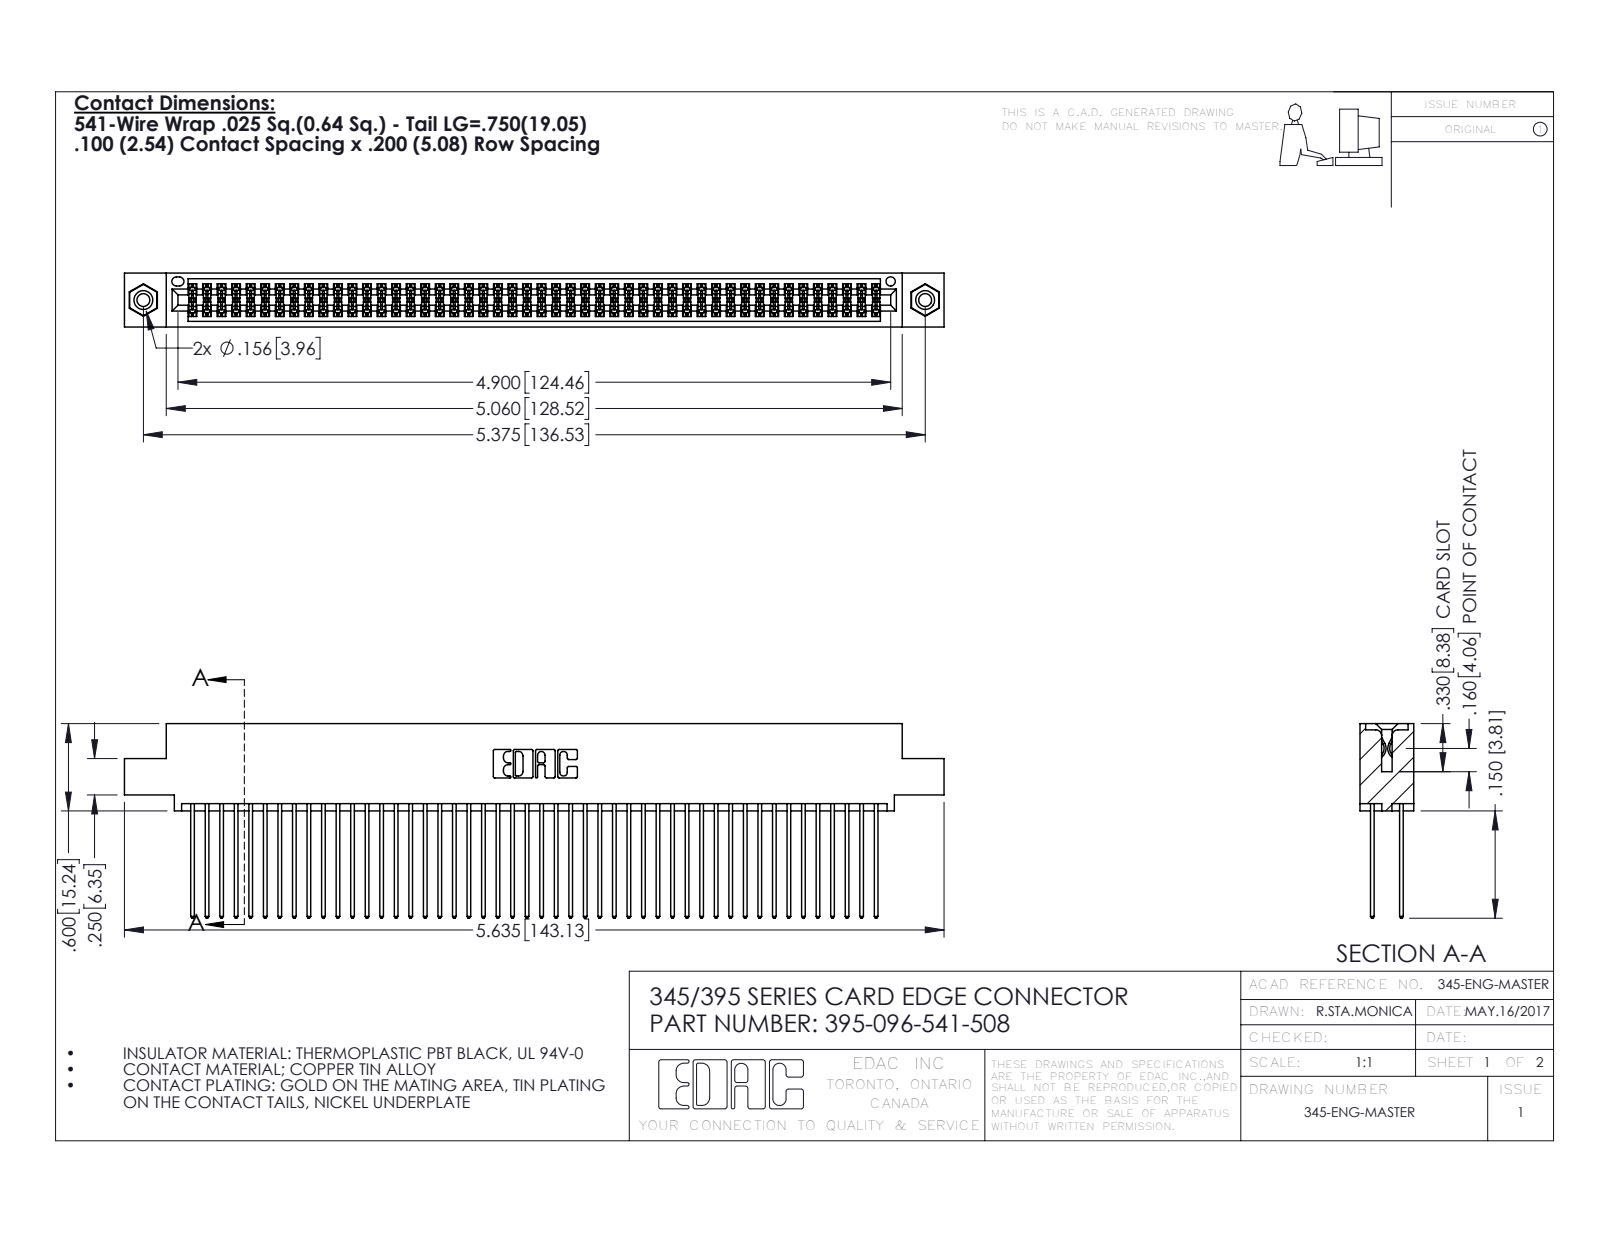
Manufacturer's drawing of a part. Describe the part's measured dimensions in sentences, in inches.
The part is named "345 Part_0.110 Offset - 0.156 Dia-TI; 345-292-001_345-293-141; 345-250-001_345-250-003-102; 395-096-541-508". Its 3-D file was written by "SolidWorks 2016 (CONFIG_CONTROL_DESIGN)". It is 99 solids with 4990 faces: 3284 planar, 1690 cylindrical and 16 other. Overall it measures 5.635 by 1.337 by 0.37 inches. Its volume is 0.881 cubic inches and its surface area 37.42 square inches. Round holes: 2 of diameter 0.089, 2 of diameter 0.125, 2 of diameter 0.156, 1 of diameter 0.064. Round bosses or shafts: 2 of diameter 0.155. Partial cylindrical surfaces (rounded edges, fillets, slot ends): 144 of radius 0.006, 96 of radius 0.01, 22 of radius 0.01, 6 of radius 0.007, 6 of radius 0.031, 3 of radius 0.026, 2 of radius 0.014, 2 of radius 0.019. The main face-to-face distances are 0.072, 0.298, 0.2, 0.098, 0.272, 0.025, 0.225, 0.37, 0.175, 0.149. The hole center spacings are 0.27, 5.139, 5.375.
